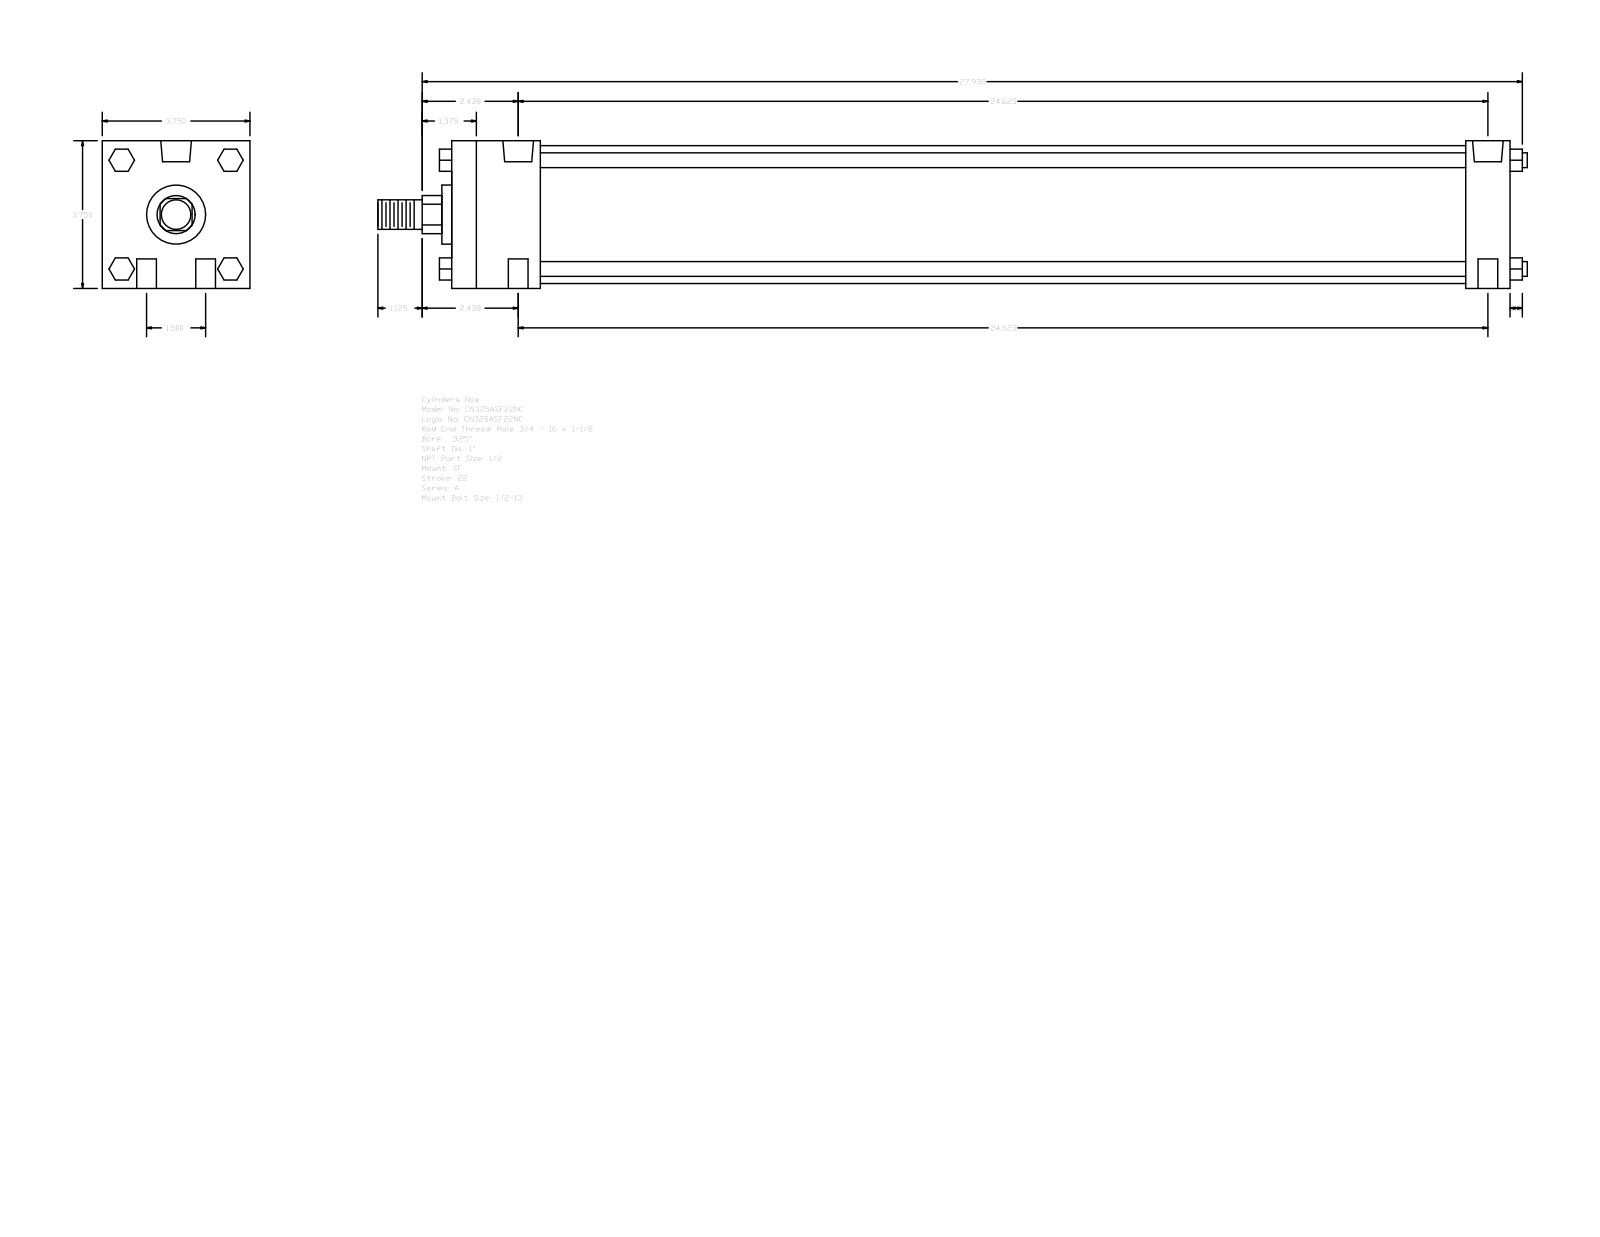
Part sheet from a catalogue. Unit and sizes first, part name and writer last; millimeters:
Units: millimetres
Overall size (bounding box): 741.36 × 95.25 × 95.25
Round holes (diameter × count): ⌀12.7 ×4, ⌀8.73 ×2, ⌀19.77 ×2
Round bosses / shafts (diameter × count): ⌀9.53 ×4, ⌀88.9 ×1, ⌀38.1 ×1, ⌀25.4 ×1, ⌀19.05 ×1
Partial cylindrical surfaces — rounded edges, fillets, slot ends (radius × count): R12.29 ×1
Main face-to-face distances: 95.24, 682.62, 28.57, 654.05, 57.15, 596.9, 625.47, 14.28, 35.05, 60.71
Hole centre spacings: 19.05, 625.77, 625.48, 38.1, 626.64, 619.12
Bodies: 0 solids, 124 faces (94 planar, 30 cylindrical, 0 other)
Part name (STEP PRODUCT): A_SF__0325_1
STEP written by: GSSL Pune (CONFIG_CONTROL_DESIGN)
